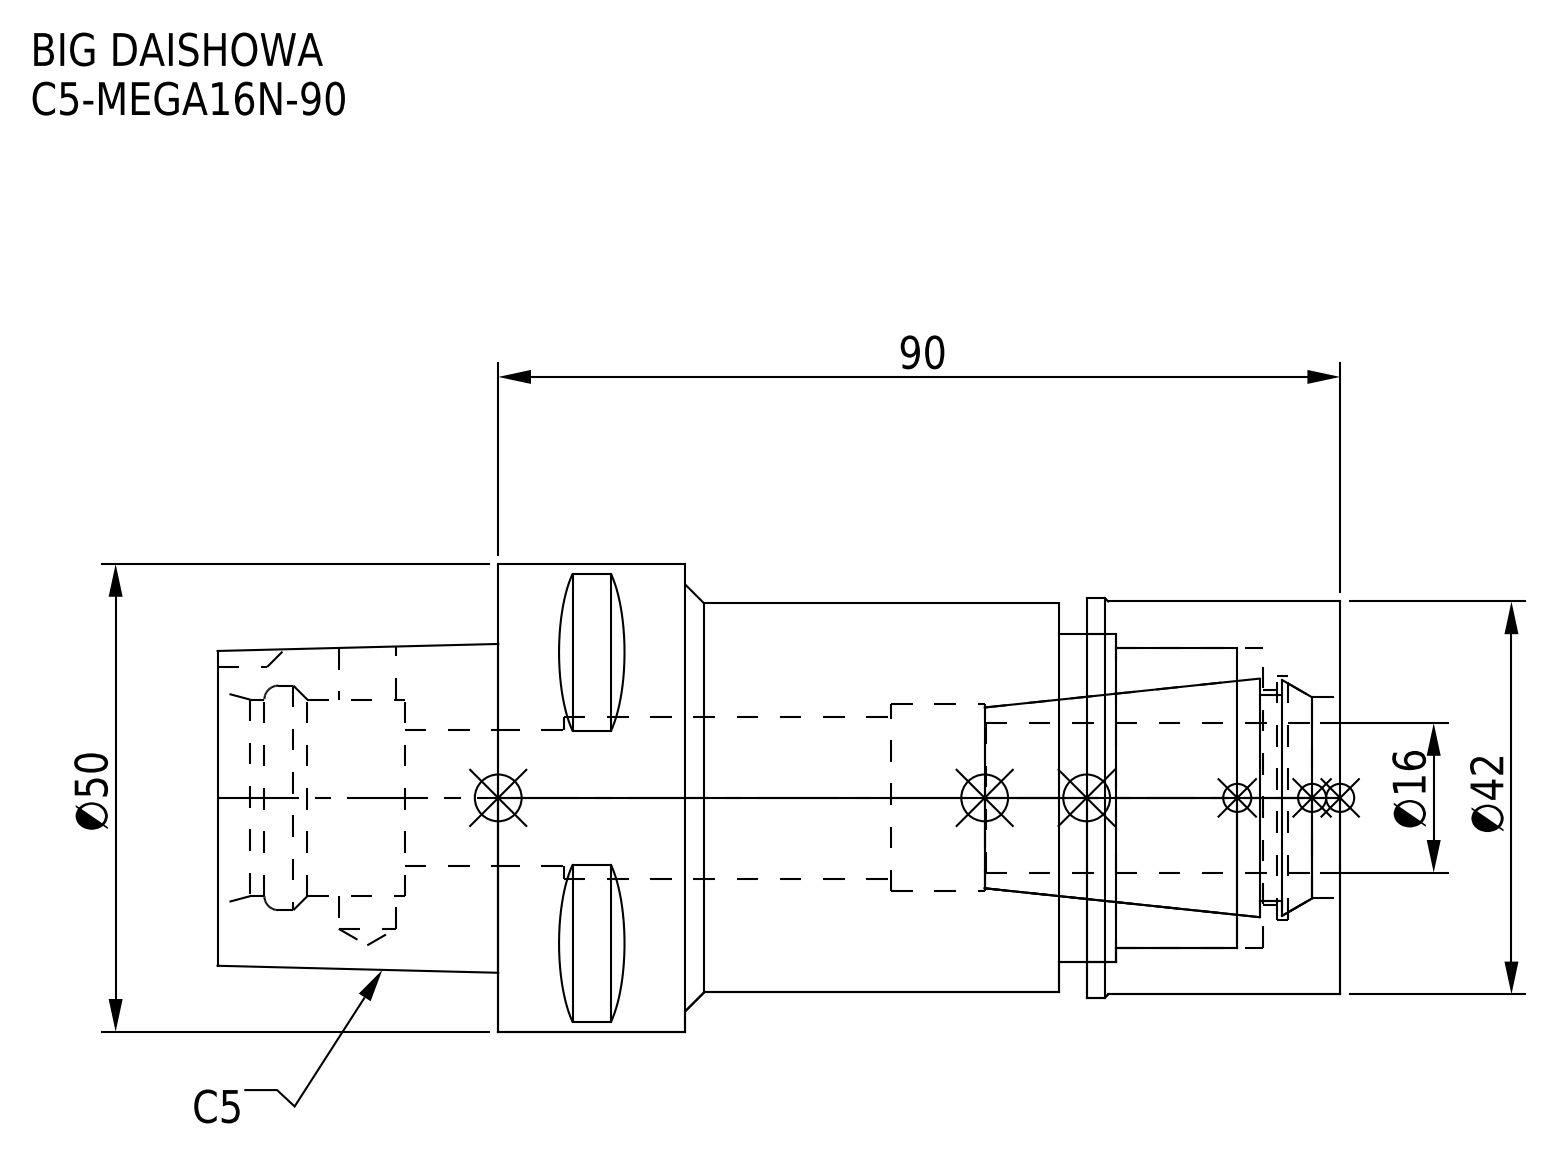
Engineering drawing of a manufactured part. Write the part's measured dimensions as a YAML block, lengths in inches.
part_name: "C5-MEGA16N-90; C5-MEGA16N-90-160-FreeParts; C5-MEGA16N-90-160.stp; C5-MEGA16N-90_1.stp (+3 more)"
step_written_by: "SolidWorks 2019 (CONFIG_CONTROL_DESIGN)"
units: inches
bodies: {solids: 2, faces: 95, planar: 38, cylindrical: 39, other: 18}
overall_size: [4.724, 1.969, 1.969]
volume: 7.498
surface_area: 49.73
round_holes:
  - {diameter: 0.24, count: 1}
  - {diameter: 0.571, count: 1}
  - {diameter: 0.681, count: 1}
  - {diameter: 0.787, count: 1}
  - {diameter: 0.827, count: 1}
  - {diameter: 0.846, count: 1}
  - {diameter: 0.906, count: 1}
  - {diameter: 0.945, count: 1}
  - {diameter: 1.024, count: 1}
  - {diameter: 1.26, count: 1}
  - {diameter: 1.378, count: 1}
round_bosses_or_shafts:
  - {diameter: 1.969, count: 1}
  - {diameter: 1.681, count: 1}
  - {diameter: 1.654, count: 1}
  - {diameter: 1.638, count: 1}
partial_cylinders:
  - {radius: 0.157, count: 1}
face_to_face_distances: [3.543, 1.181, 0.787, 1.067, 2.476, 1.185, 0.118, 2.358, 0.945, 0.323]
